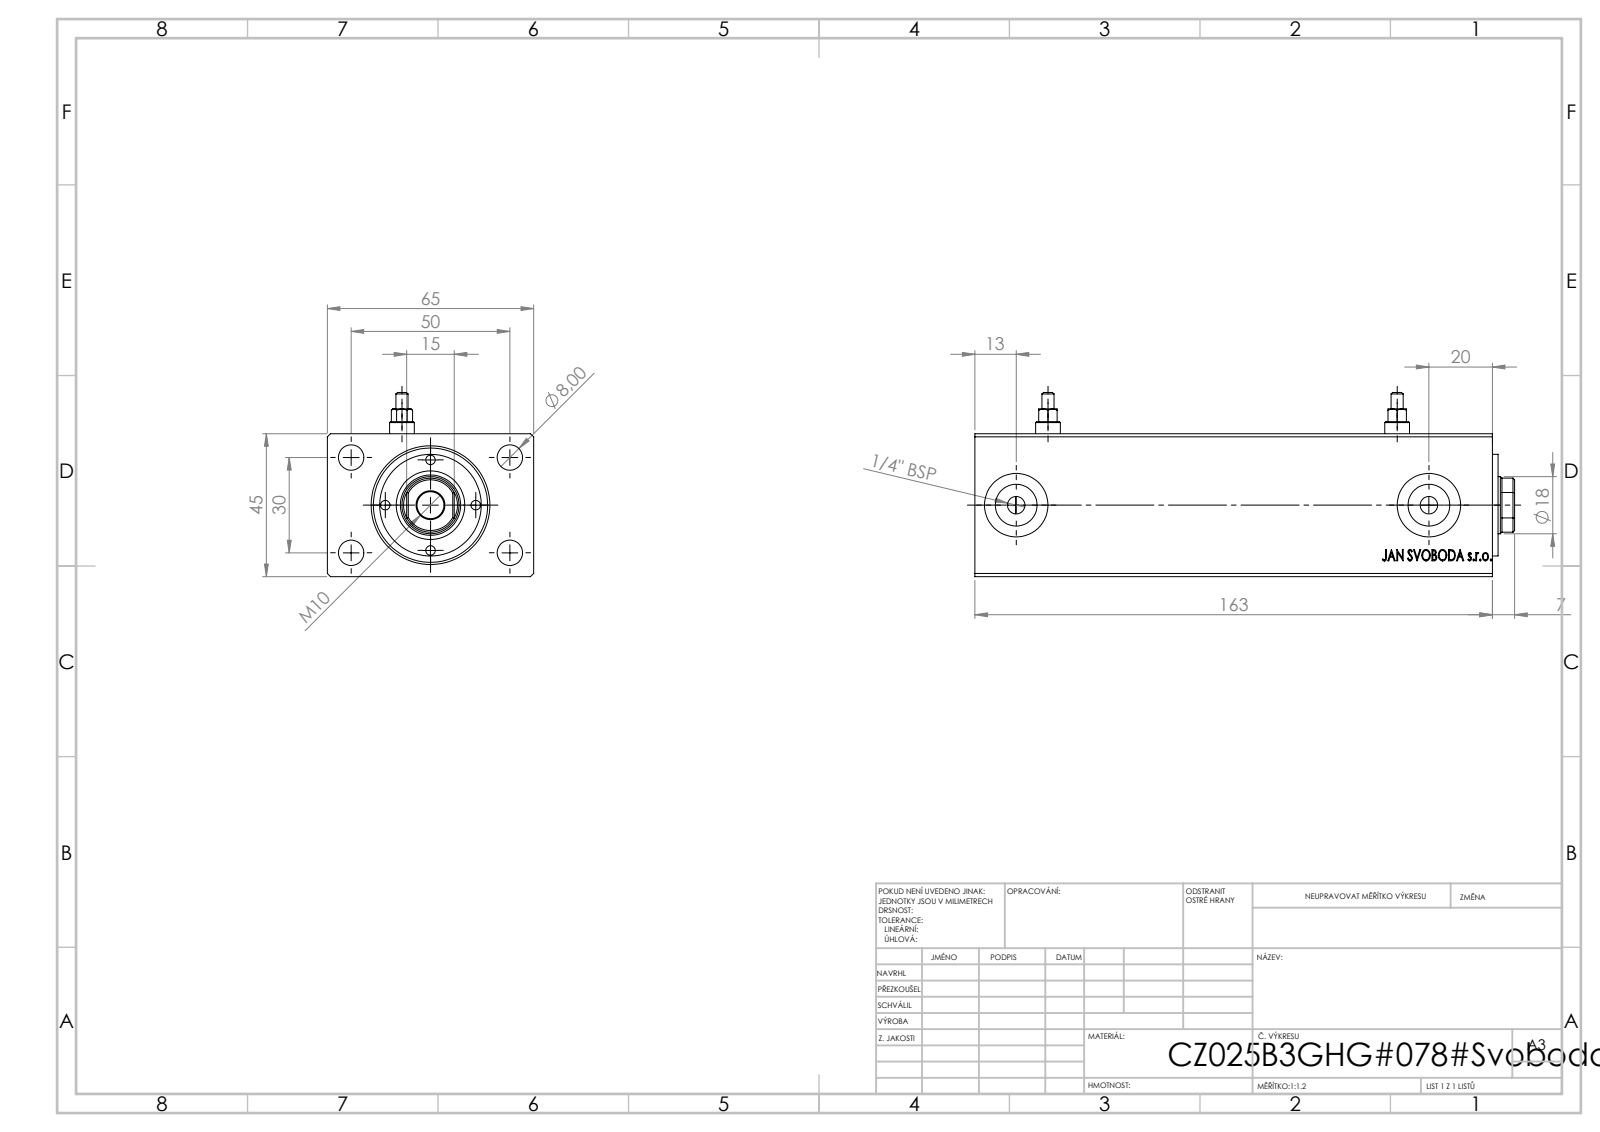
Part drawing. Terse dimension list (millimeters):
name: V500CZ; V500CZ_B_VC; Zatka_Cushioning3
written by: SolidWorks 2019 (CONFIG_CONTROL_DESIGN)
unit: mm
bodies: 5 solids, 933 faces (423 planar, 74 cylindrical, 436 other)
size: 170 × 65 × 58
volume: 444 411 mm³; area: 74 884 mm²
holes: 6× ⌀8, 4× ⌀3, 2× ⌀1.8, 2× ⌀5.5, 2× ⌀13.16, 2× ⌀20, 1× ⌀8.5, 1× ⌀18, 1× ⌀19, 1× ⌀25, 1× ⌀36
bosses: 2× ⌀7.8, 2× ⌀3.8, 1× ⌀32
rounds: 1× R8.5
face distances: 45, 65, 163, 7, 162.8, 12.8, 150.2, 12.6, 1.8, 5.2
hole spacings: 14.25, 18.45, 20.15, 25.01, 29.15, 38.48, 42.02, 28.5
